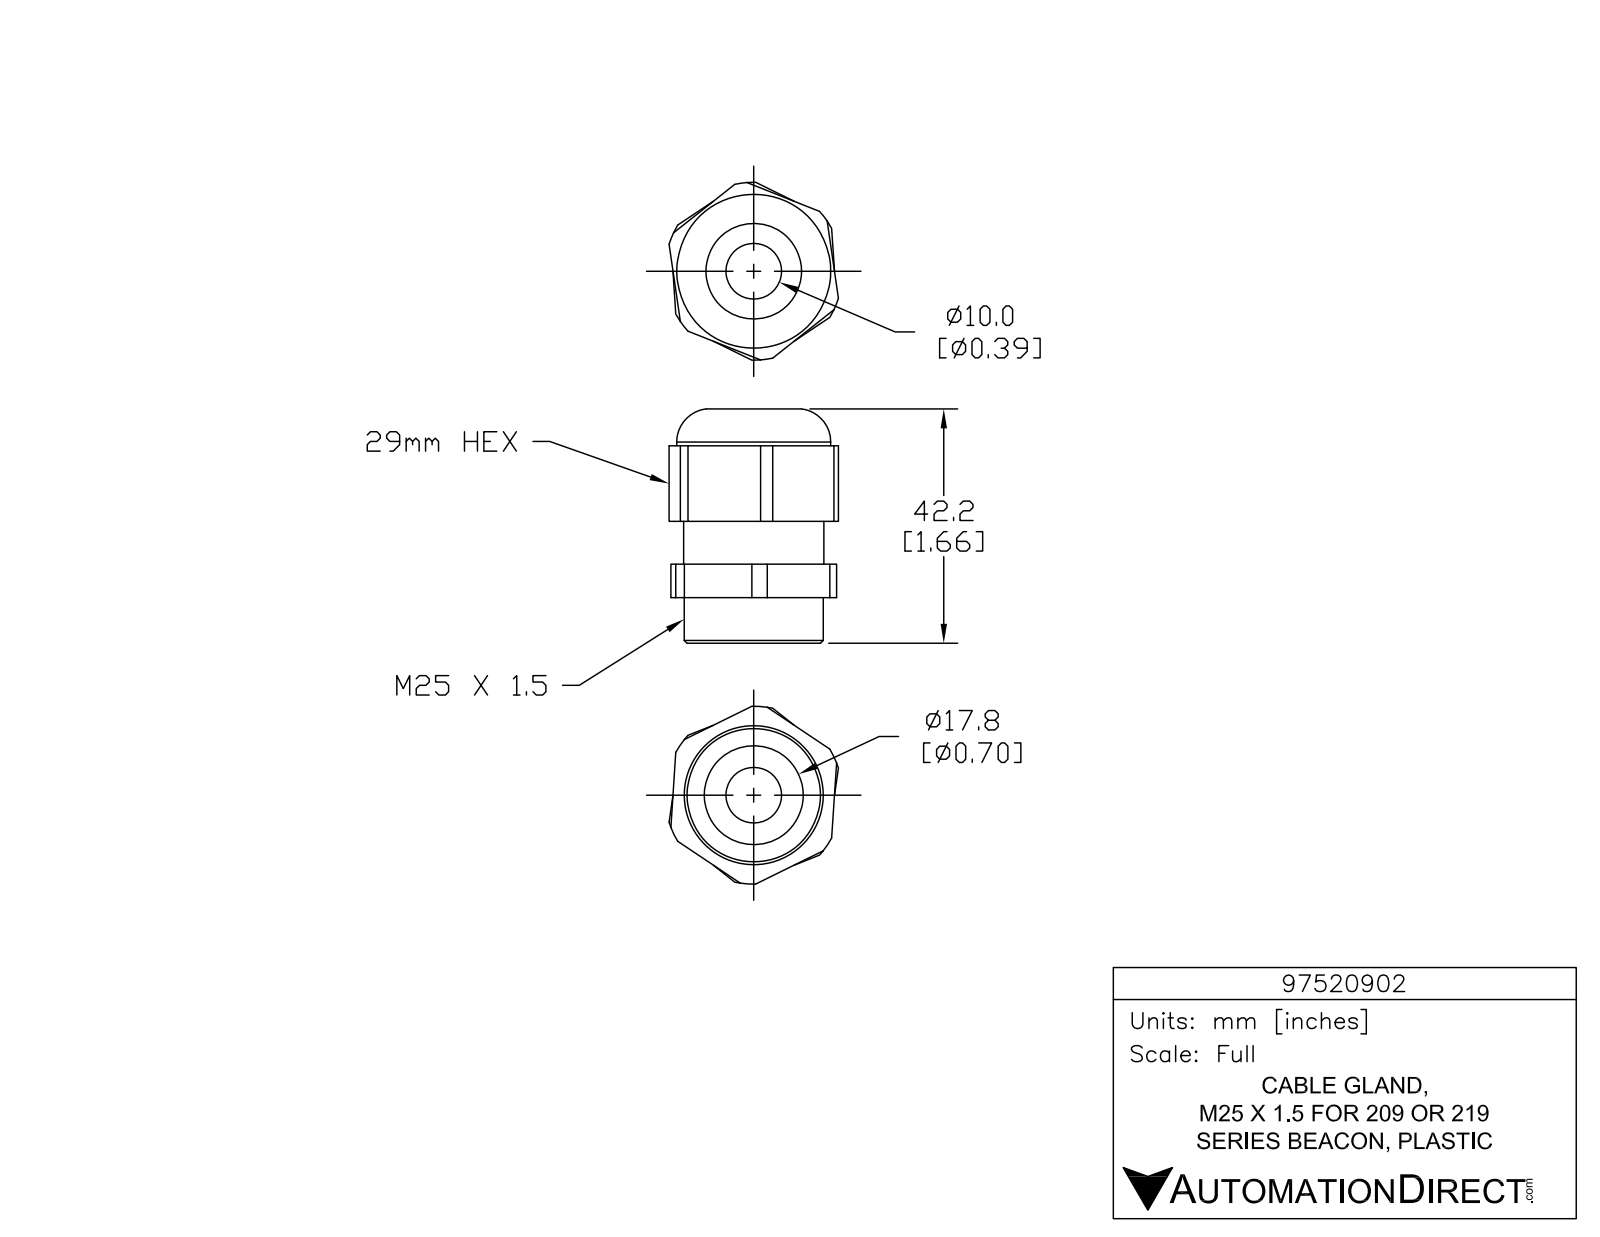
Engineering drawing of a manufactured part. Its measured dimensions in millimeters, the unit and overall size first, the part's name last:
Units: millimetres
Overall size (bounding box): 42.15 × 32 × 30.49
Round holes (diameter × count): ⌀10 ×1, ⌀17.2 ×1, ⌀17.8 ×1
Round bosses / shafts (diameter × count): ⌀27.7 ×1, ⌀25.25 ×1, ⌀25 ×1
Partial cylindrical surfaces — rounded edges, fillets, slot ends (radius × count): R16 ×1
Main face-to-face distances: 28.76, 29, 6, 13.7, 7.7, 8.22, 14.22, 21.92, 28.74, 28.6
Volume: 16 538 mm³ · Surface area: 7 309 mm²
Bodies: 1 solid, 48 faces (19 planar, 25 cylindrical, 4 other)
Part name (STEP PRODUCT): 97520902
STEP written by: SolidWorks 2017 (AUTOMOTIVE_DESIGN)
